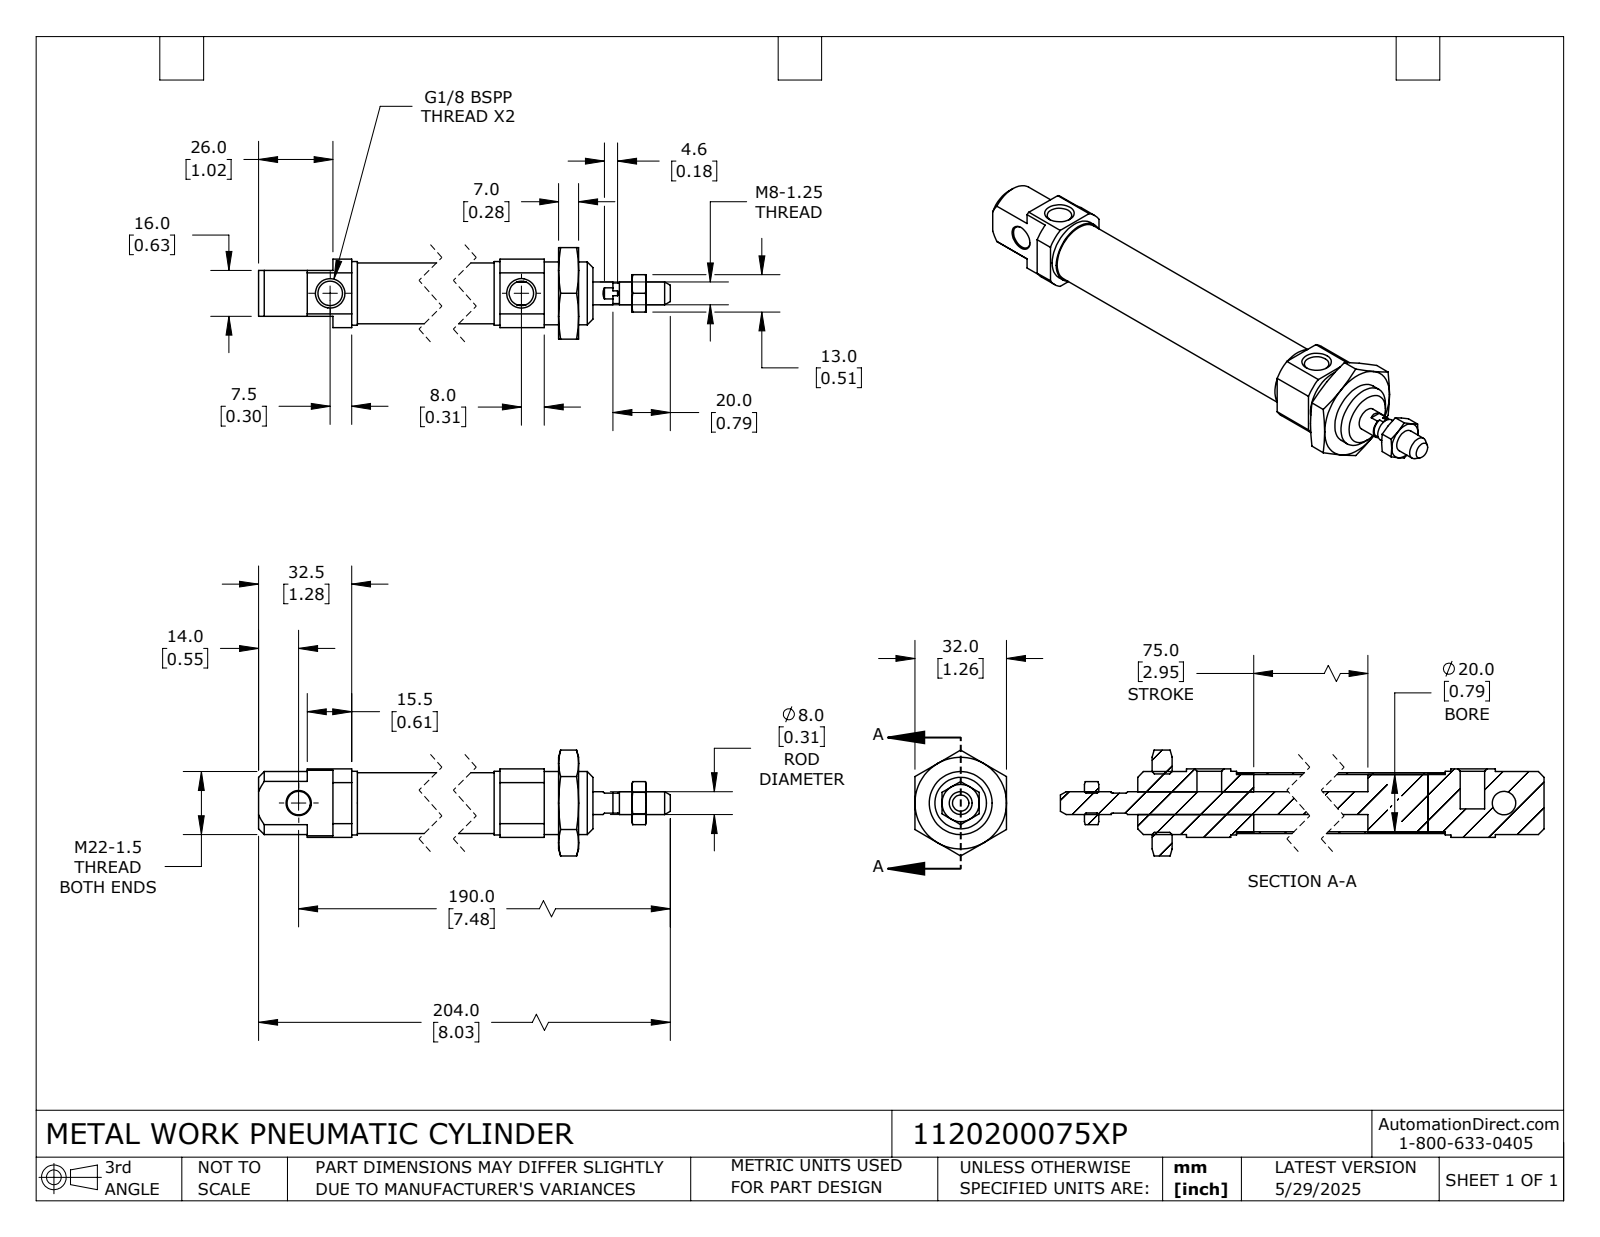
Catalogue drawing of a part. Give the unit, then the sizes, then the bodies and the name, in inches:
Units: inches
Overall size (bounding box): 8.031 × 1.455 × 1.26
Round holes (diameter × count): ⌀0.337 ×2, ⌀0.272 ×1, ⌀0.323 ×1, ⌀0.787 ×1, ⌀0.802 ×1
Round bosses / shafts (diameter × count): ⌀0.874 ×1, ⌀0.866 ×1, ⌀0.837 ×1, ⌀0.793 ×1, ⌀0.315 ×1, ⌀0.283 ×1
Partial cylindrical surfaces — rounded edges, fillets, slot ends (radius × count): R0.549 ×1
Main face-to-face distances: 0.156, 0.786, 0.943, 0.315, 1.594, 5.374, 0.276, 0.197, 5.177, 4.902
Hole centre spacings: 5
Volume: 3.086 in³ · Surface area: 49.56 in²
Bodies: 6 solids, 147 faces (56 planar, 45 cylindrical, 46 other)
Part name (STEP PRODUCT): 1120200075XP_BODY; 1120200075XP_ROD; 1120200075XP
STEP written by: SolidWorks 2024 (CONFIG_CONTROL_DESIGN)
